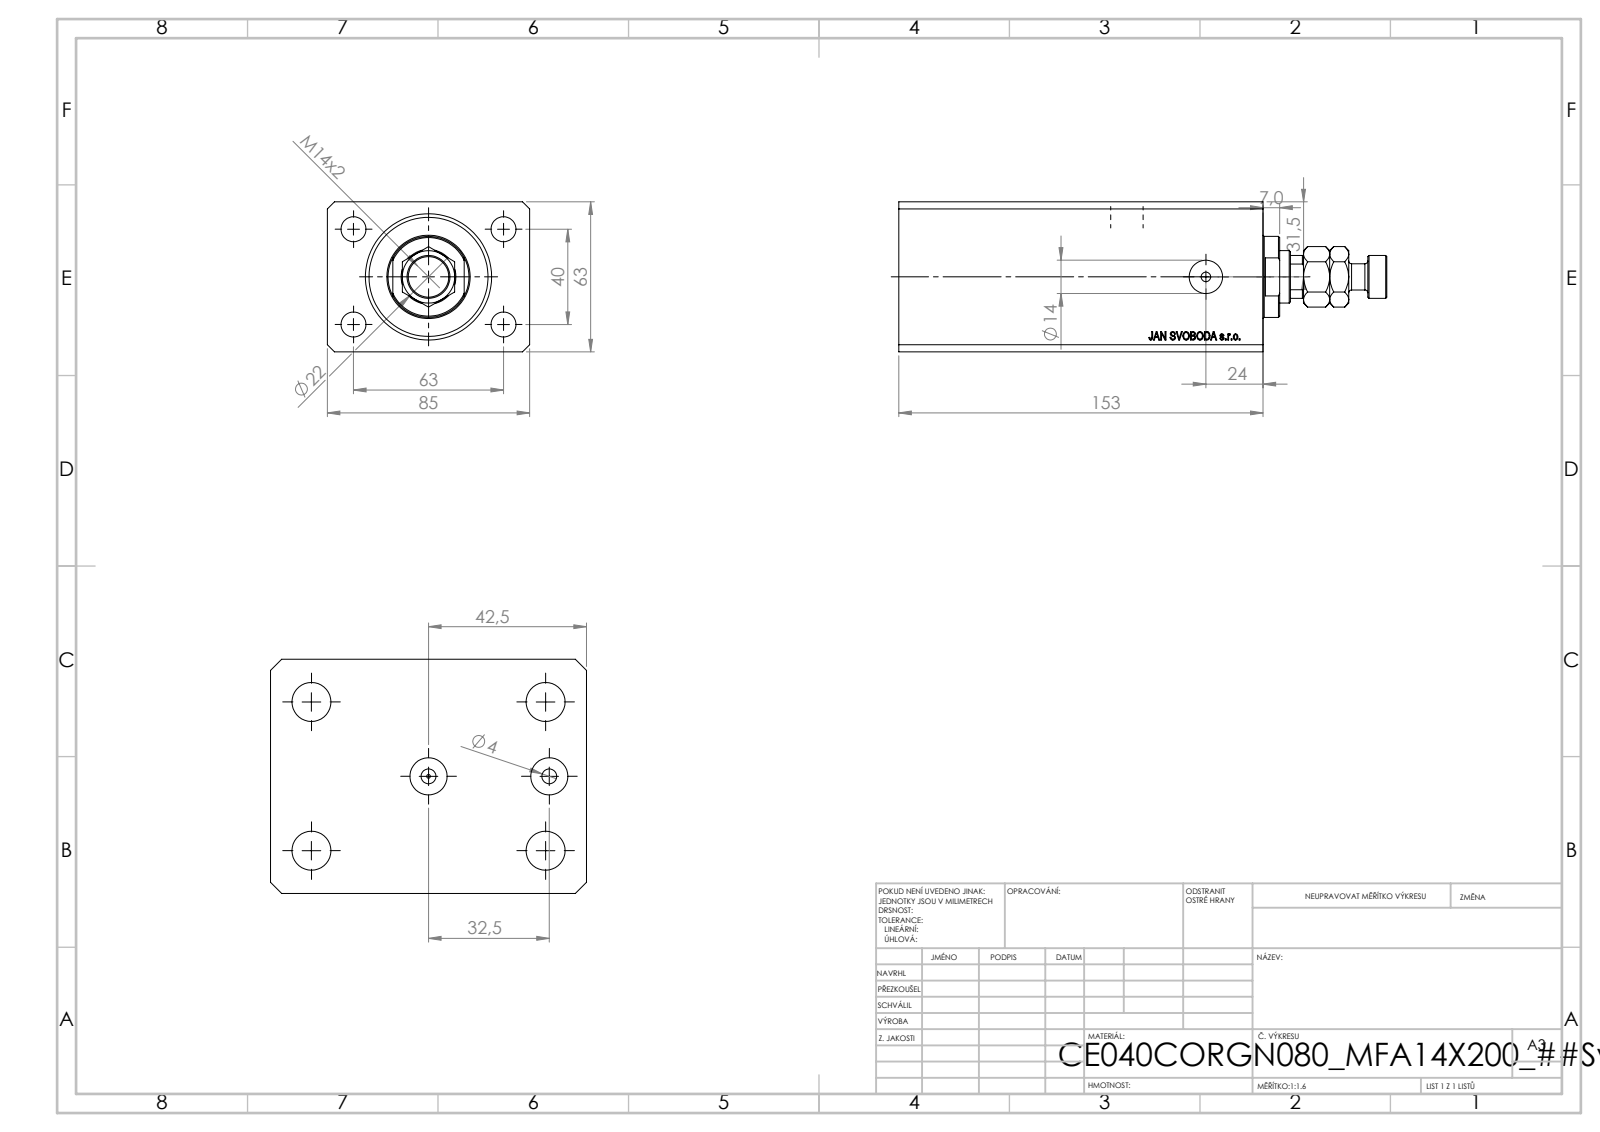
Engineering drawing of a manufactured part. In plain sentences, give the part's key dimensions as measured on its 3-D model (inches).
The part is named "V250CE_C_VCP; MFA; V250CE_C_Body; V250CE_VC_C". Its 3-D file was written by "SolidWorks 2019 (CONFIG_CONTROL_DESIGN)". It is 4 solids with 920 faces: 444 planar, 50 cylindrical and 426 other. Overall it measures 8.071 by 3.346 by 2.48 inches. Its volume is 43.15 cubic inches and its surface area 192.7 square inches. Round holes: 4 of diameter 0.157, 4 of diameter 0.413, 2 of diameter 0.394, 2 of diameter 0.551, 1 of diameter 0.049, 1 of diameter 0.492, 1 of diameter 0.866, 1 of diameter 1.575, 1 of diameter 2.087. Round bosses or shafts: 1 of diameter 1.339, 1 of diameter 0.709, 1 of diameter 0.433. Partial cylindrical surfaces (rounded edges, fillets, slot ends): 1 of radius 0.413. The main face-to-face distances are 2.48, 3.346, 6.024, 0.669, 5.354, 0.449, 4.906, 5.575, 3.953, 3.15. The hole center spacings are 1.469, 0.788, 1.575, 2.48, 2.64, 2.938, 1.28, 4.134.
